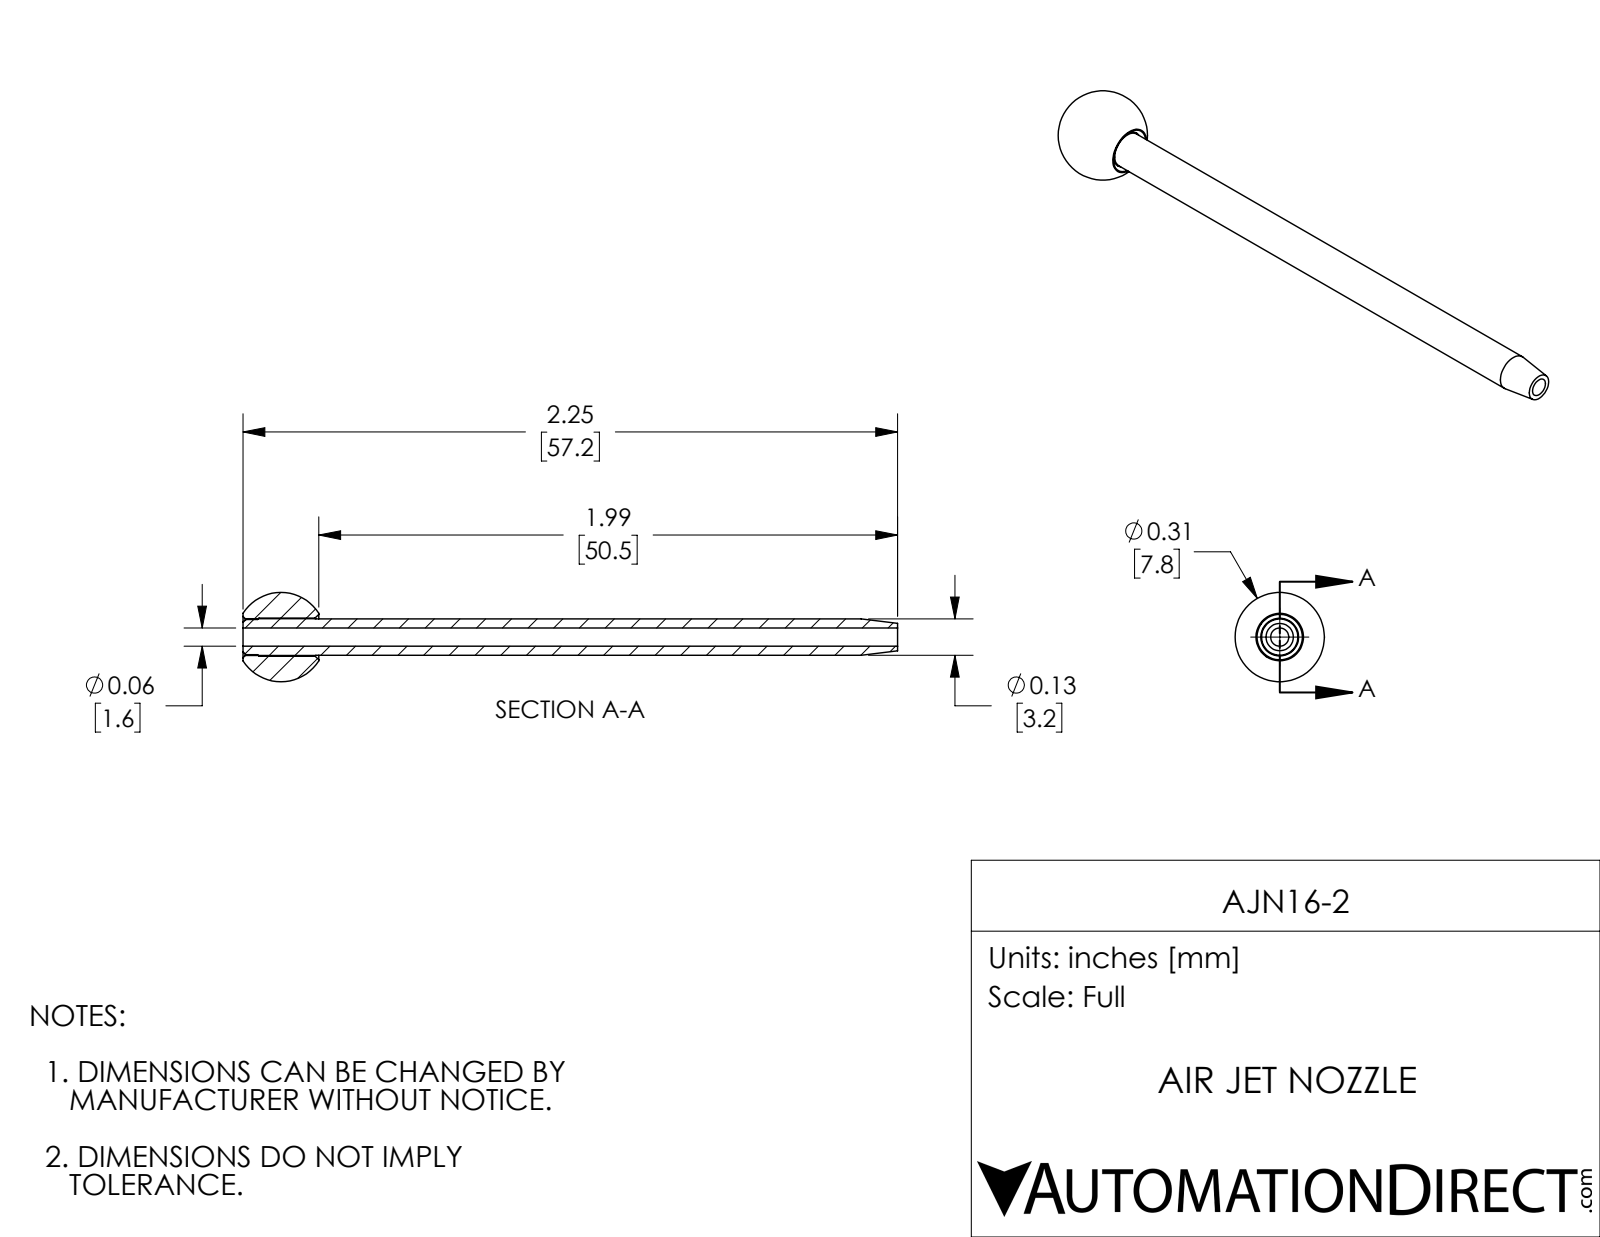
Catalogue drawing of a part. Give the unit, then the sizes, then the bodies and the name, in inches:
Units: inches
Overall size (bounding box): 2.25 × 0.307 × 0.307
Round holes (diameter × count): ⌀0.063 ×1, ⌀0.126 ×1
Round bosses / shafts (diameter × count): ⌀0.13 ×1, ⌀0.125 ×1, ⌀0.121 ×1
Main face-to-face distances: 2.25, 0.26, 1.99
Volume: 0.032 in³ · Surface area: 1.699 in²
Bodies: 2 solids, 28 faces (4 planar, 10 cylindrical, 14 other)
Part name (STEP PRODUCT): AJN16-2
STEP written by: SolidWorks 2018 (AUTOMOTIVE_DESIGN)
